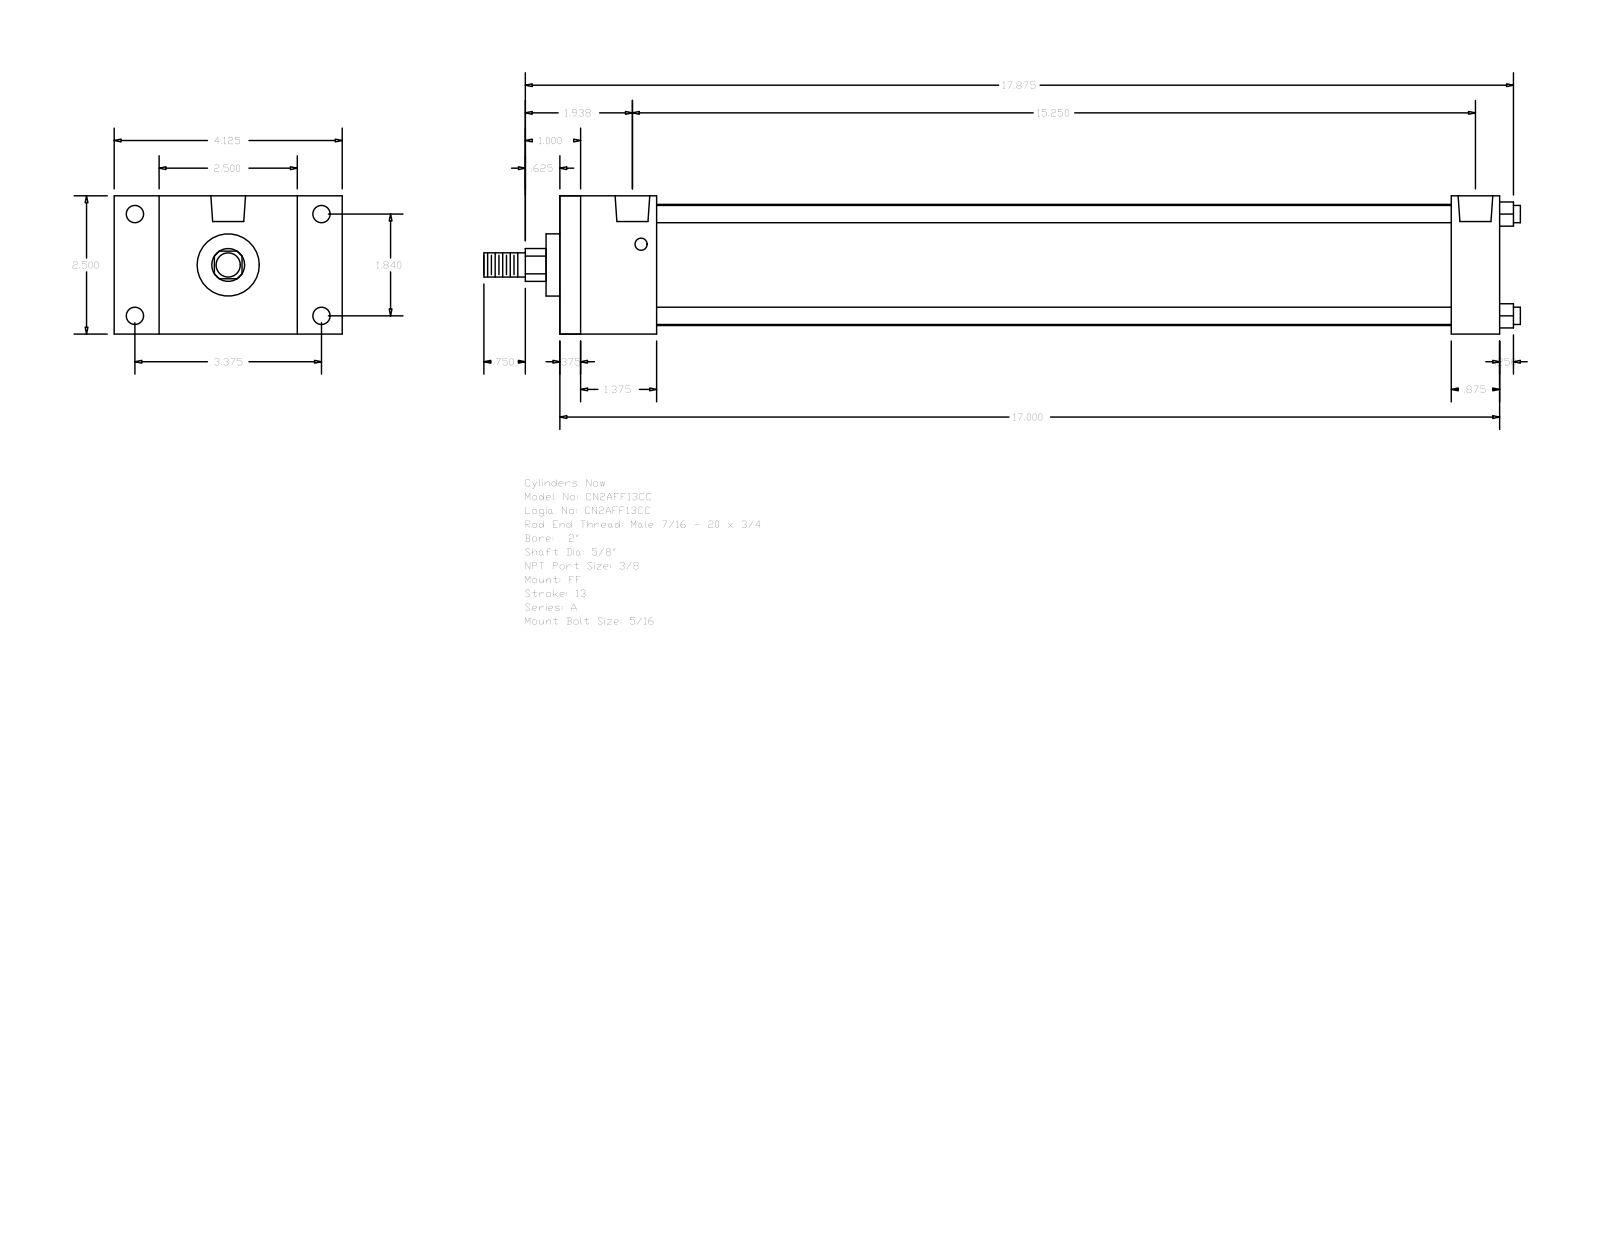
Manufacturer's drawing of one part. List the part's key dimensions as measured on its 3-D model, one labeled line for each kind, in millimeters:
Part name (STEP PRODUCT): A_FF__0200_0.625
STEP written by: GSSL Pune (CONFIG_CONTROL_DESIGN)
Units: millimetres
Bodies: 0 solids, 92 faces (64 planar, 28 cylindrical, 0 other)
Overall size (bounding box): 476.25 × 104.78 × 63.5
Round holes (diameter × count): ⌀5.56 ×4, ⌀7.94 ×4, ⌀15.93 ×2
Round bosses / shafts (diameter × count): ⌀7.94 ×4, ⌀55.63 ×1, ⌀28.57 ×1, ⌀15.88 ×1, ⌀11.11 ×1
Partial cylindrical surfaces — rounded edges, fillets, slot ends (radius × count): R7.54 ×1
Main face-to-face distances: 63.5, 431.8, 9.52, 422.28, 34.93, 44.45, 409.57, 400.05, 365.12, 387.35
Hole centre spacings: 46.74, 85.72, 97.63, 379.4, 3.97, 3.98, 383.37, 383.38
